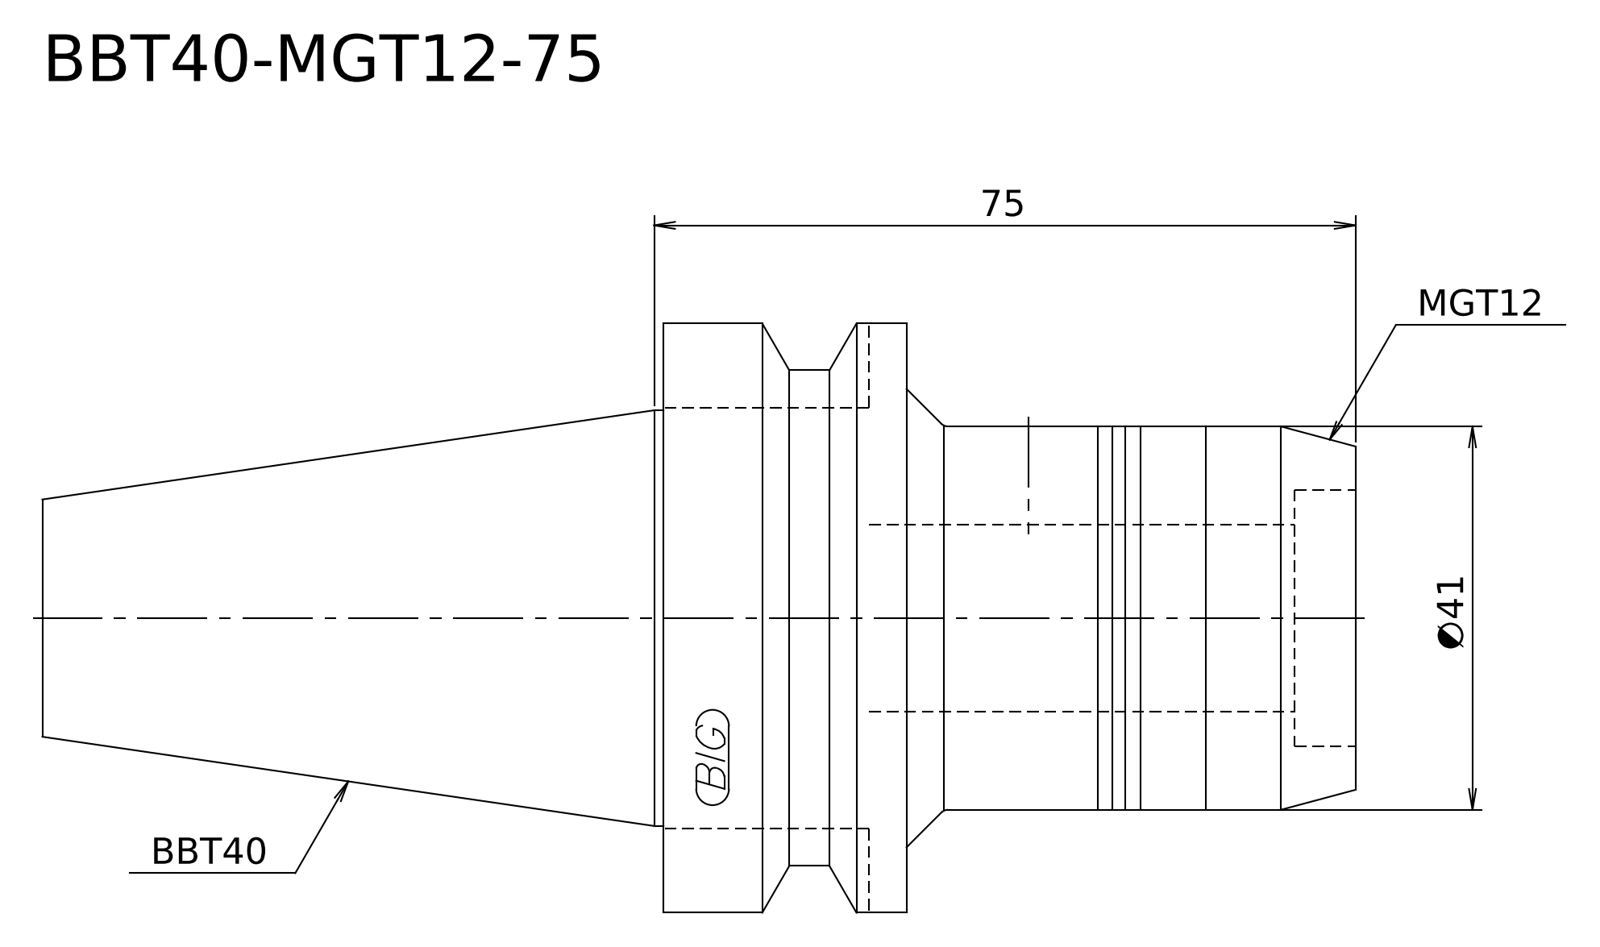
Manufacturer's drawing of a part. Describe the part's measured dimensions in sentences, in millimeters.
Its 3-D file was written by "Kubotek KeyCreator V8.5.1 (14335) (CONFIG_CONTROL_DESIGN)". It is 1 solid with 14 faces: 4 planar, 5 cylindrical and 5 other. Overall it measures 140.4 by 63 by 63 millimeters. Its volume is 203 613 cubic millimeters and its surface area 24 172 square millimeters. Round bosses or shafts: 1 of diameter 63, 1 of diameter 53, 1 of diameter 44.45, 1 of diameter 41. The main face-to-face distances are 26, 48, 74, 140.4, 92.4, 66.4.
